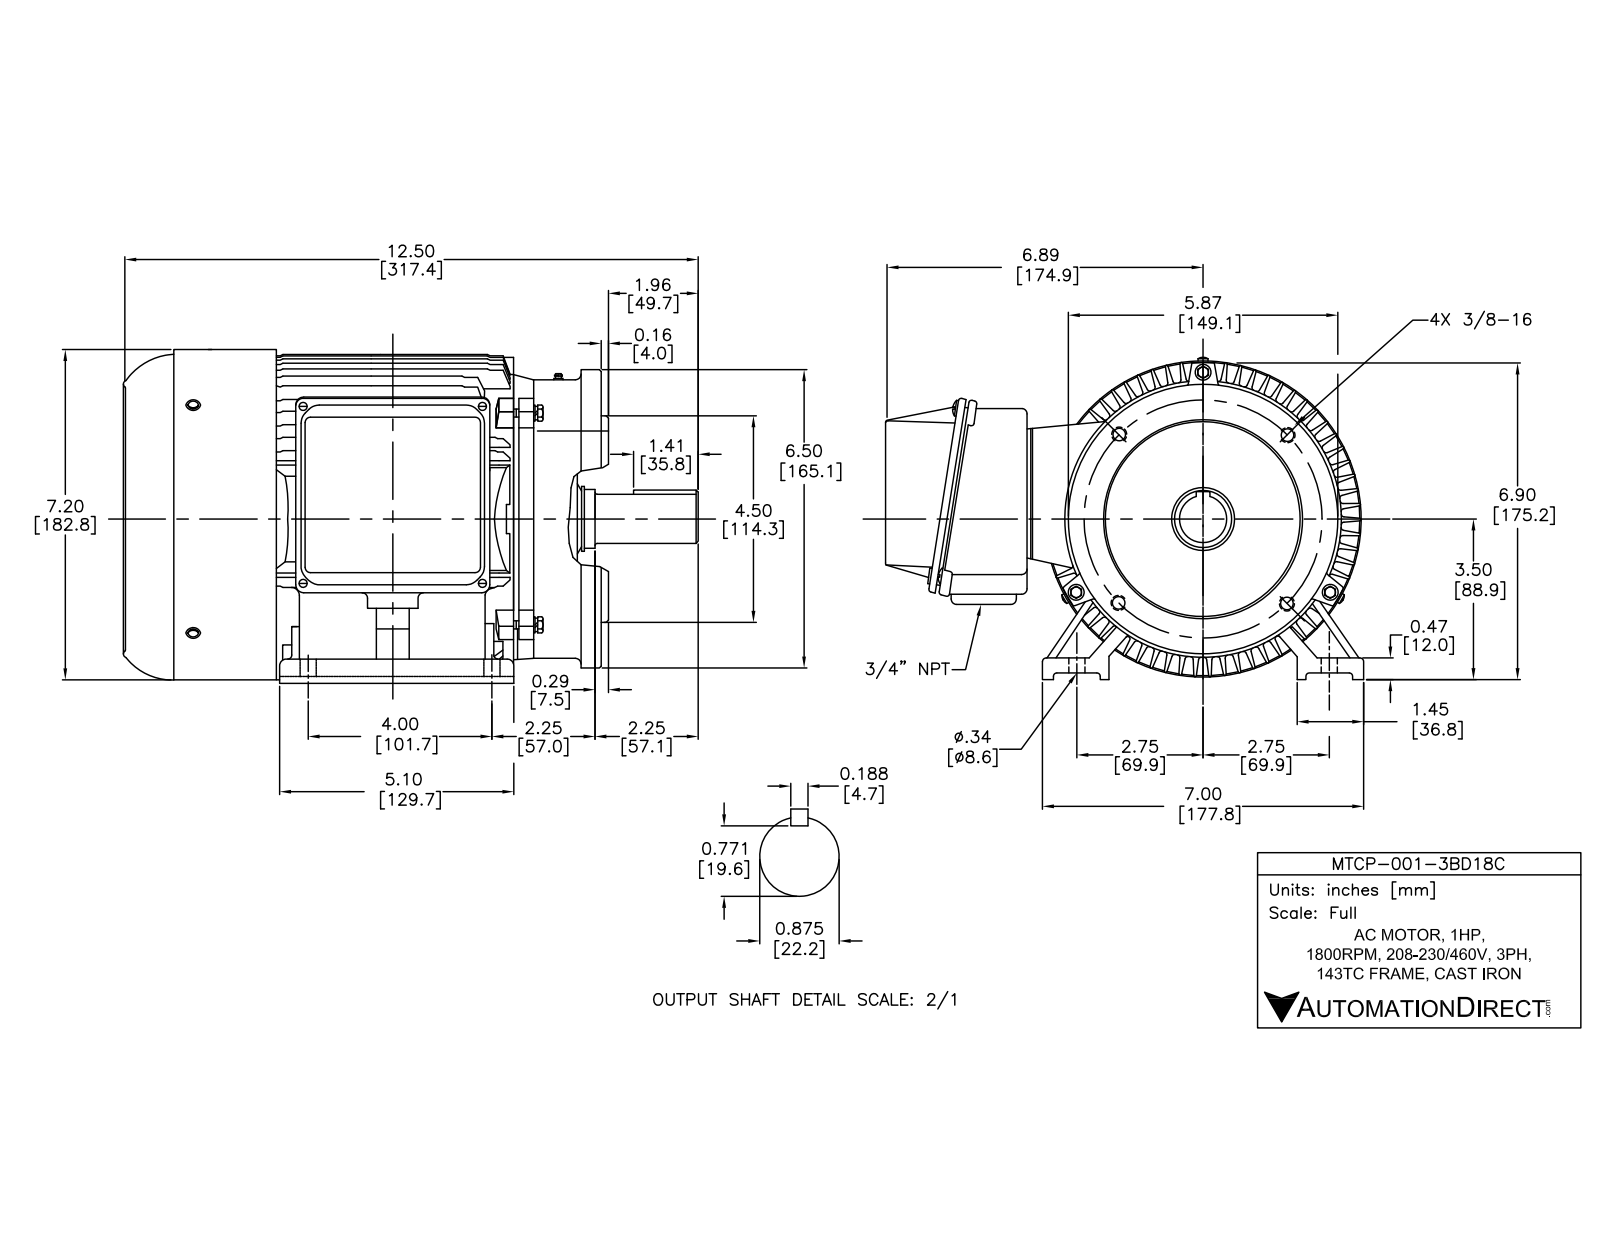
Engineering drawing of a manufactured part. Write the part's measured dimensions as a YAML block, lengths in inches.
part_name: "plain washers-n series-grade a gb_GB_FASTENER_WASHER_PWNA 5; plain washers-n series-grade a gb_GB_FASTENER_WASHER_PWNA 6; PE140接线盒座_默认_按加工; hex head bolts-full thread grade c gb_GB_FASTENER_BOLT_HHBFTC M5X10-N (+5 more)"
step_written_by: "SolidWorks 2017 (AUTOMOTIVE_DESIGN)"
units: inches
bodies: {solids: 47, faces: 2398, planar: 667, cylindrical: 959, other: 772}
overall_size: [13.841, 9.716, 7.181]
volume: 115.3
surface_area: 1086
round_holes:
  - {diameter: 0.228, count: 14}
  - {diameter: 0.165, count: 11}
  - {diameter: 0.354, count: 8}
  - {diameter: 0.079, count: 4}
  - {diameter: 0.313, count: 4}
  - {diameter: 0.197, count: 3}
  - {diameter: 0.209, count: 3}
  - {diameter: 0.213, count: 3}
  - {diameter: 0.252, count: 3}
  - {diameter: 0.263, count: 3}
  - {diameter: 0.276, count: 3}
  - {diameter: 0.303, count: 3}
round_bosses_or_shafts:
  - {diameter: 0.197, count: 11}
  - {diameter: 0.472, count: 3}
  - {diameter: 0.394, count: 3}
  - {diameter: 0.389, count: 3}
  - {diameter: 0.315, count: 3}
  - {diameter: 0.236, count: 3}
  - {diameter: 6.906, count: 1}
  - {diameter: 6.811, count: 1}
partial_cylinders:
  - {radius: 0.02, count: 176}
  - {radius: 0.039, count: 67}
  - {radius: 0.079, count: 54}
  - {radius: 0.049, count: 27}
  - {radius: 0.276, count: 24}
  - {radius: 0.013, count: 16}
  - {radius: 0.118, count: 15}
  - {radius: 0.02, count: 14}
face_to_face_distances: [0.157, 0.047, 0.472, 0.079, 0.236, 11.591, 11.543, 2.561, 2.514, 9.03]
hole_center_spacings: [2.126, 3.543, 1, 2.937, 3.007, 4, 4.154, 5.5]
